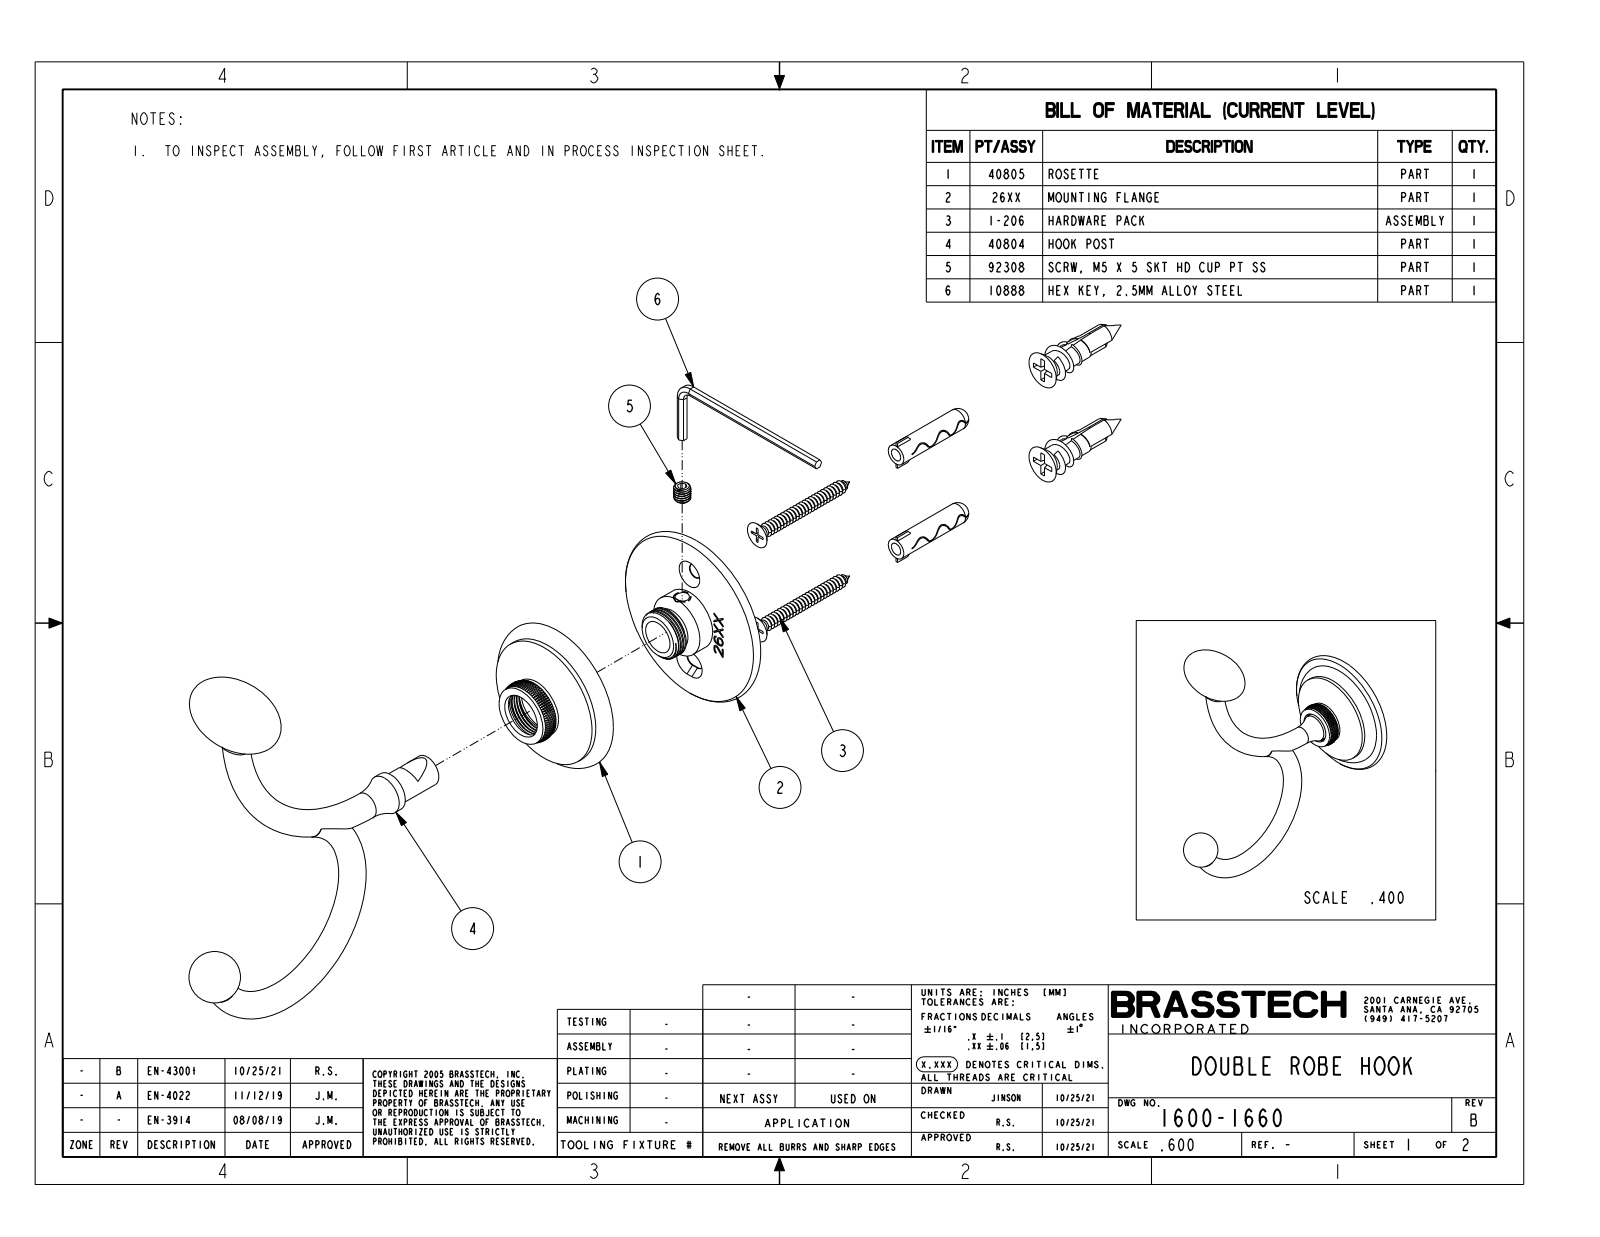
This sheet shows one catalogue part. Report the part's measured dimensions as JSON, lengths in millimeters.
{"part_name": "1600-1660", "step_written_by": "CREO PARAMETRIC BY PTC INC, 2018400 (CONFIG_CONTROL_DESIGN)", "units": "millimeters", "bodies": {"solids": 1, "faces": 274, "planar": 164, "cylindrical": 8, "other": 102}, "overall_size": [123.4, 96, 54], "volume_mm3": 36020, "surface_area_mm2": 12940, "round_bosses_or_shafts": [[39.4, 1], [18, 1], [11.9, 1]], "face_to_face_distances": [3, 18, 15, 6.9, 6.9]}
